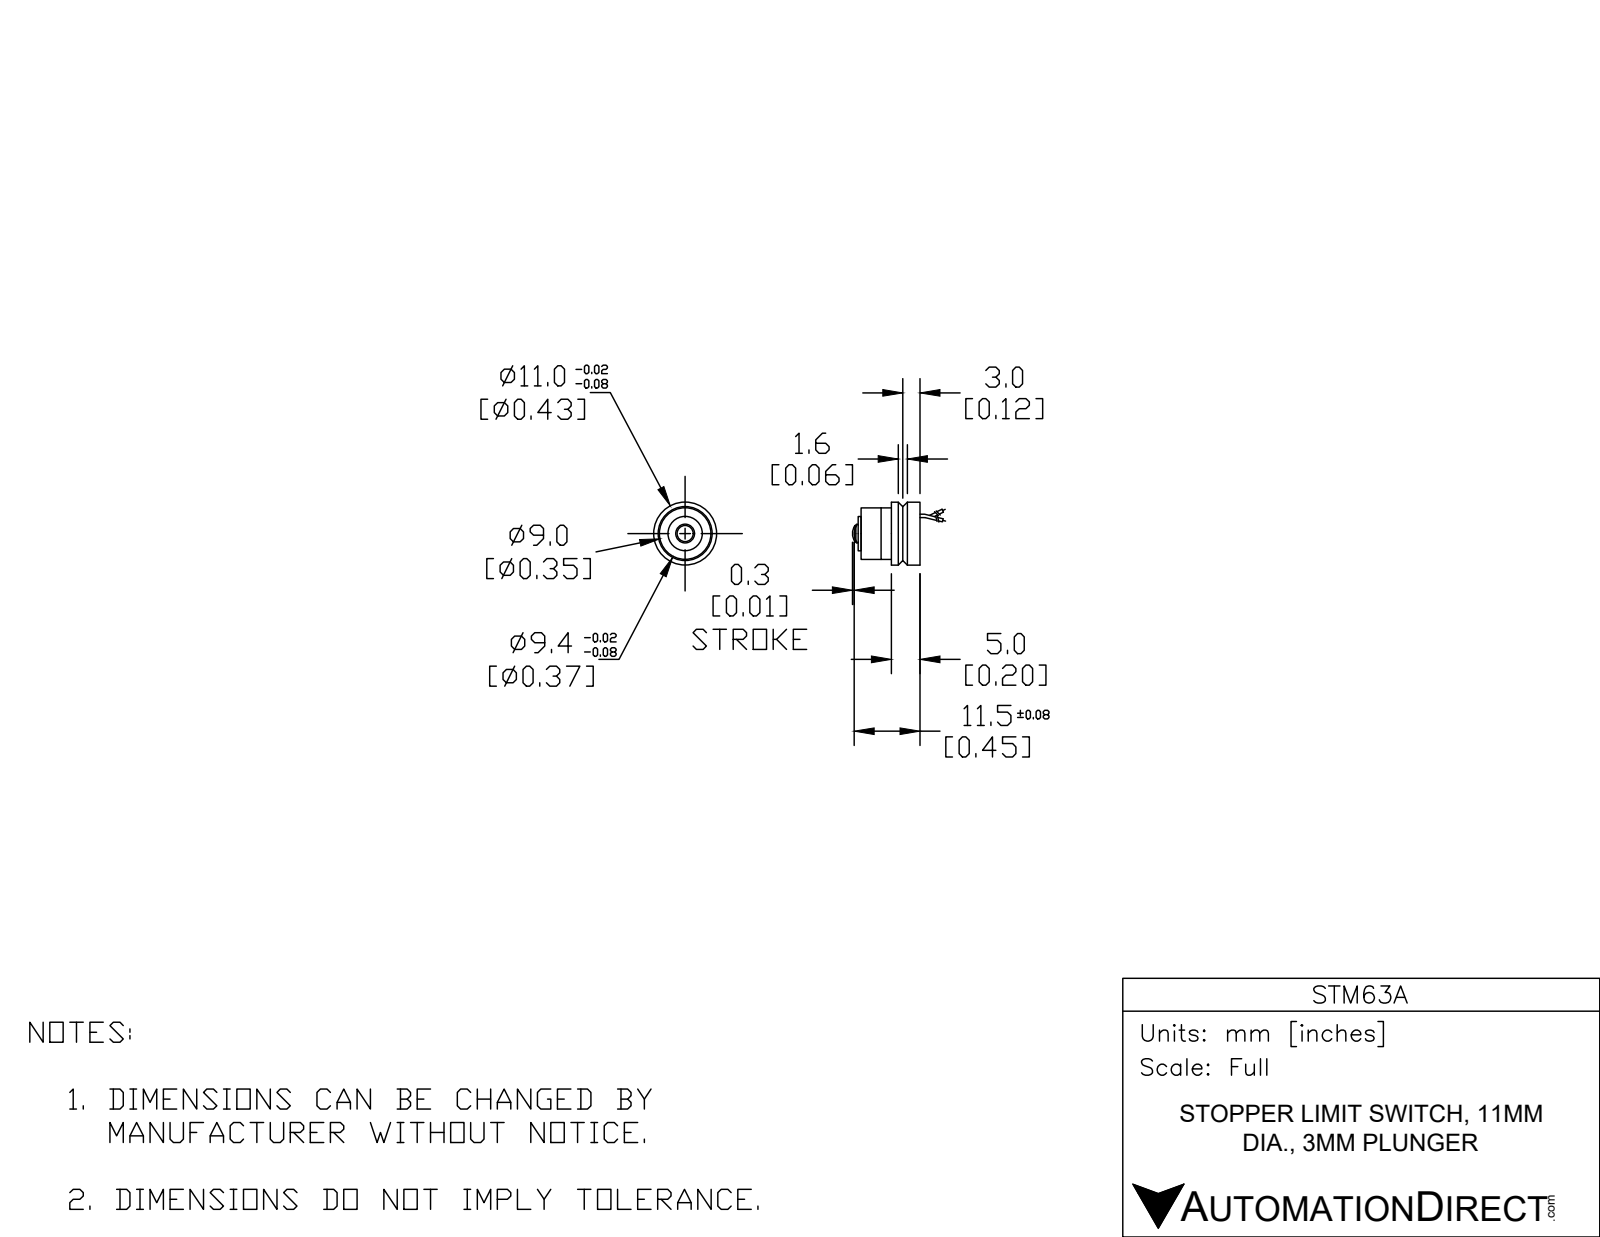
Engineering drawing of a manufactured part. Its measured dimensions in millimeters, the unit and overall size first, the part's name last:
Units: millimetres
Overall size (bounding box): 21.8 × 11 × 11
Round bosses / shafts (diameter × count): ⌀0.6 ×2, ⌀11 ×1, ⌀9 ×1, ⌀8.8 ×1, ⌀6 ×1, ⌀2.8 ×1
Main face-to-face distances: 10.3, 5.3, 5, 5.5, 10.5, 0.5, 5.8, 10.8, 4, 3.7
Volume: 803 mm³ · Surface area: 625 mm²
Bodies: 1 solid, 37 faces (9 planar, 18 cylindrical, 10 other)
STEP written by: Spatial InterOp 3D (CONFIG_CONTROL_DESIGN)
